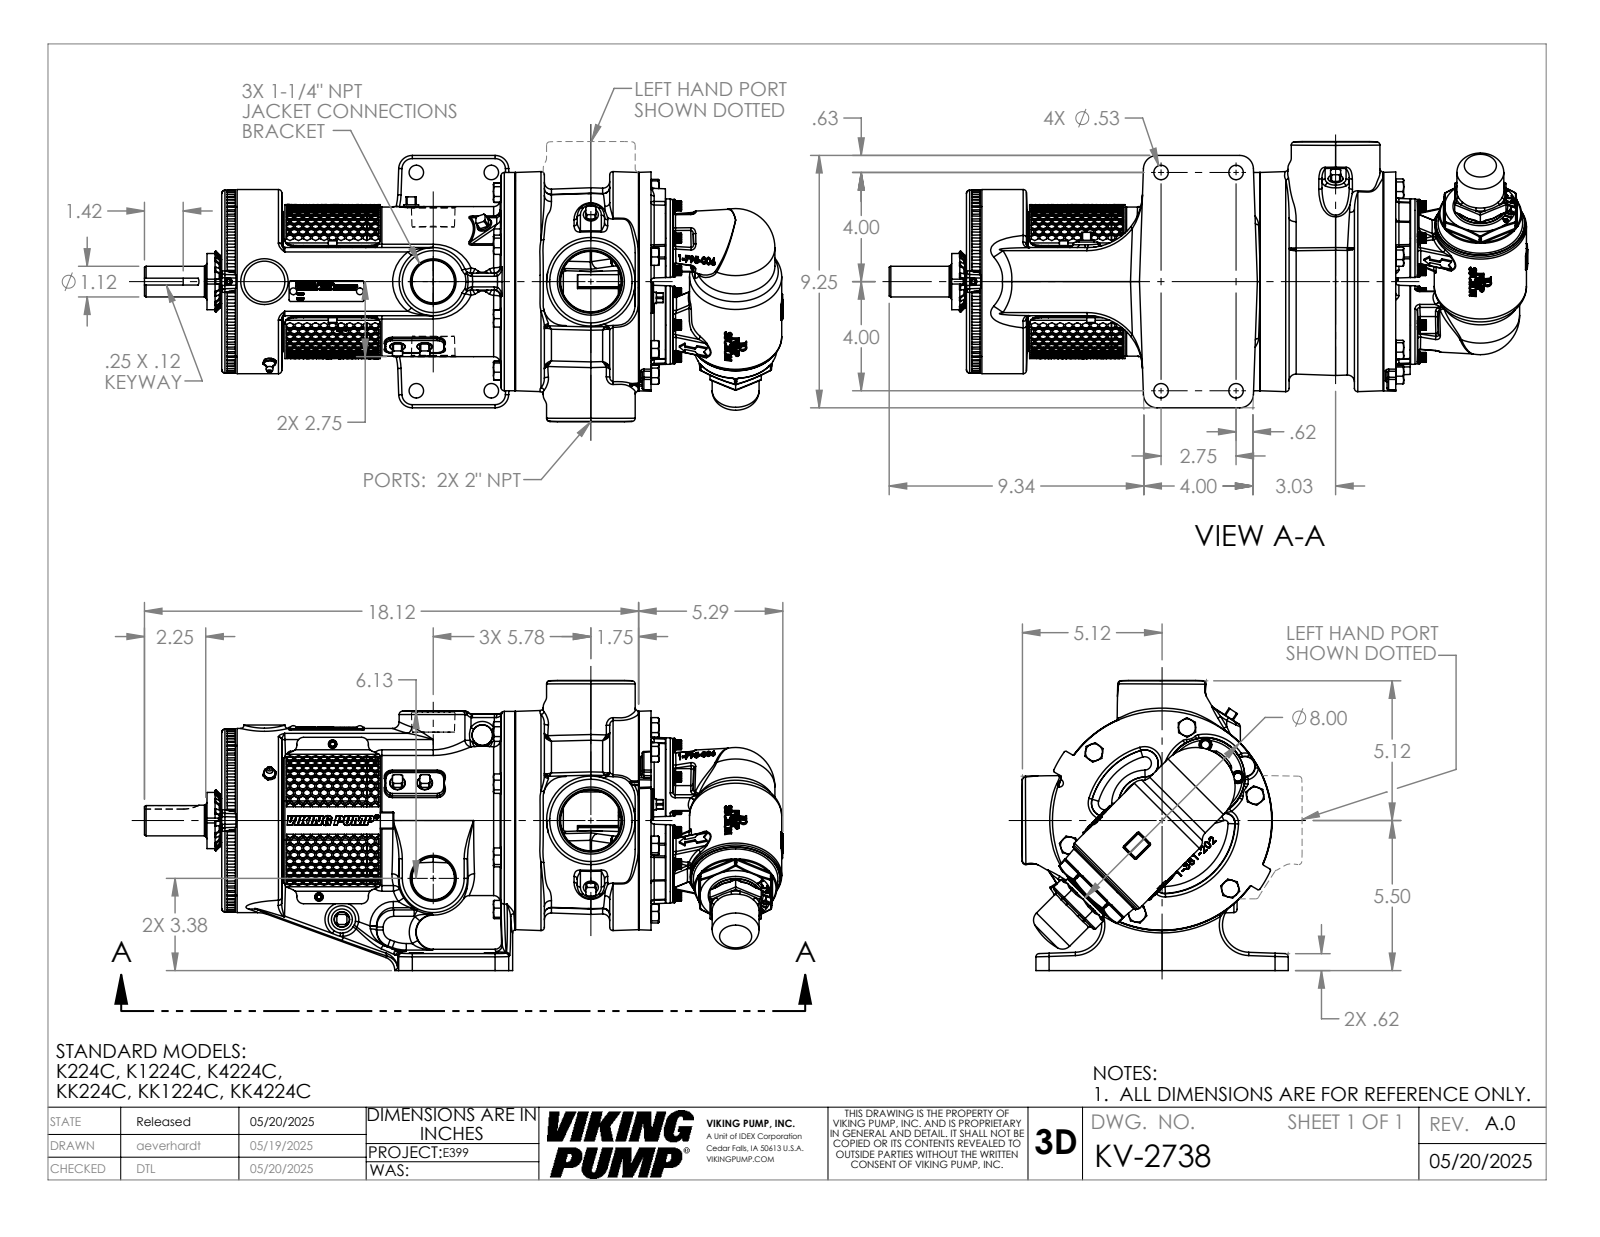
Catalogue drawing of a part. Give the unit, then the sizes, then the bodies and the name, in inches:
Units: inches
Overall size (bounding box): 23.407 × 10.634 × 9.759
Round holes (diameter × count): ⌀0.34 ×8, ⌀0.344 ×8, ⌀0.78 ×8, ⌀0.197 ×6, ⌀0.25 ×6, ⌀0.531 ×4, ⌀0.159 ×2, ⌀0.313 ×2, ⌀0.257 ×1, ⌀0.453 ×1, ⌀1.38 ×1, ⌀1.387 ×1
Round bosses / shafts (diameter × count): ⌀0.625 ×10, ⌀0.469 ×8, ⌀0.313 ×8, ⌀2.88 ×5, ⌀0.625 ×4, ⌀0.437 ×3, ⌀0.312 ×3, ⌀8 ×1
Partial cylindrical surfaces — rounded edges, fillets, slot ends (radius × count): R0.12 ×39, R0.03 ×37, R0.24 ×22, R0.12 ×16, R0.5 ×10, R0.06 ×8, R0.09 ×8, R0.178 ×8
Main face-to-face distances: 10.425, 4.75, 5.315, 15.74, 0.75, 4, 0.565, 15.175, 0.5, 1.5
Hole centre spacings: 1.03, 3, 1.376, 2.385, 2.909, 3.531, 3.655, 3.799
Volume: 612.6 in³ · Surface area: 1 031 in²
Bodies: 1 solid, 5053 faces (1728 planar, 673 cylindrical, 2652 other)
Part name (STEP PRODUCT): KV-2738
STEP written by: SolidWorks 2024 (AUTOMOTIVE_DESIGN)
